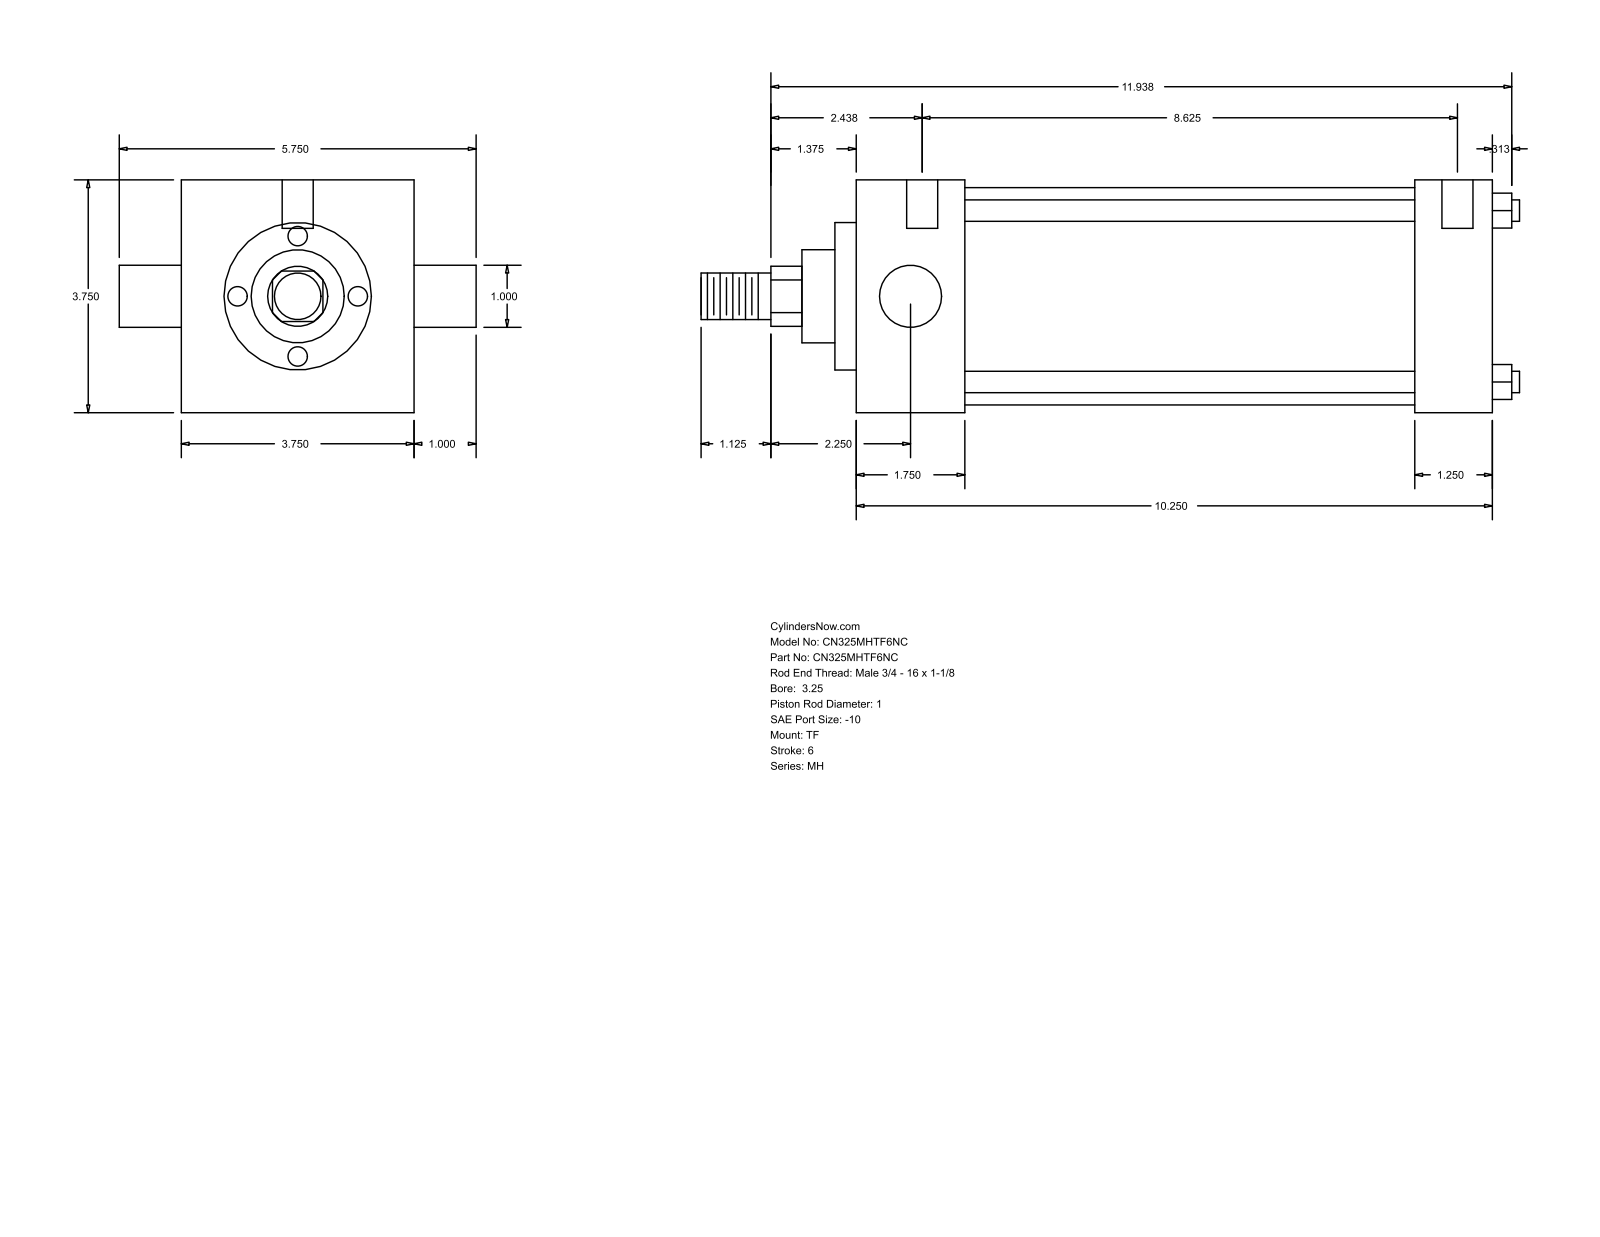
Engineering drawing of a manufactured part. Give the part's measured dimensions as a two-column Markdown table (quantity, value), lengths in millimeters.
| quantity | value |
| --- | --- |
| part name | MH_TF__0325_1 |
| STEP written by | GSSL Pune (CONFIG_CONTROL_DESIGN) |
| units | millimeters |
| bodies | 0 solids, 86 faces (61 planar, 25 cylindrical, 0 other) |
| overall size | 334.96 × 146.05 × 95.25 |
| round holes (diameter × count) | 5.56 × 3, 12.7 × 2 |
| round bosses / shafts (diameter × count) | 8.76 × 4, 25.4 × 2, 88.9 × 1, 60.33 × 1, 38.1 × 1, 19.05 × 1 |
| partial cylindrical surfaces (radius × count) | 12.29 × 1 |
| main face-to-face distances | 95.24, 260.35, 44.46, 228.6, 184.14, 215.89, 31.75, 8.73, 53.19, 237.33 |
| hole center spacings | 1.58, 4.76, 219.08, 220.66, 223.84, 225.42 |
